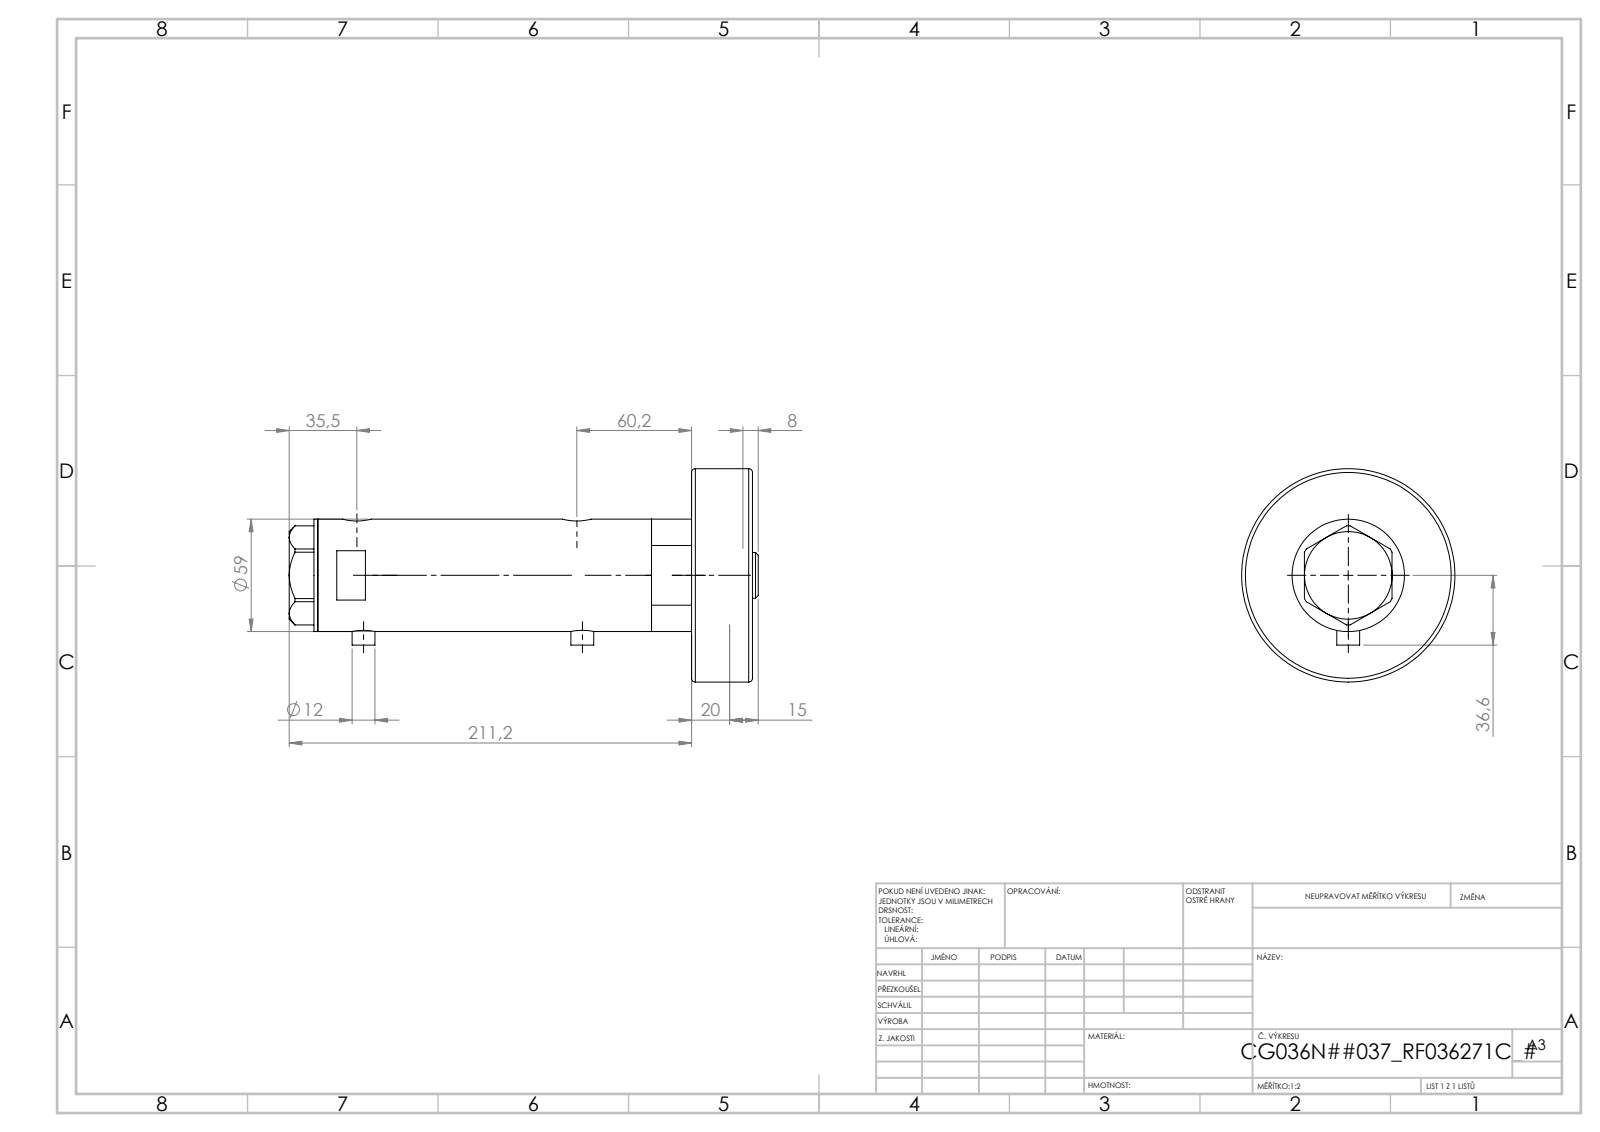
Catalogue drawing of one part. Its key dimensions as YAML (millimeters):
part_name: "V270CG_BACK; V270CG_MIDDLE; V270CG_VC; V270CG_FRONT"
step_written_by: "SolidWorks 2019 (CONFIG_CONTROL_DESIGN)"
units: millimeters
bodies: {solids: 4, faces: 126, planar: 53, cylindrical: 53, other: 20}
overall_size: [200.42, 60.1, 59]
volume: 452799
surface_area: 95842
round_holes:
  - {diameter: 5, count: 2}
  - {diameter: 9.73, count: 2}
  - {diameter: 12.5, count: 2}
  - {diameter: 15, count: 2}
  - {diameter: 8.5, count: 1}
  - {diameter: 25, count: 1}
  - {diameter: 26.5, count: 1}
  - {diameter: 36, count: 1}
  - {diameter: 40, count: 1}
  - {diameter: 52, count: 1}
round_bosses_or_shafts:
  - {diameter: 12, count: 2}
  - {diameter: 59, count: 1}
  - {diameter: 48, count: 1}
  - {diameter: 46, count: 1}
  - {diameter: 24, count: 1}
face_to_face_distances: [94.34, 23.5, 70.84, 15, 38.5, 109.34, 185.42, 170.42, 146.92, 76.08]
hole_center_spacings: [2.9, 3.5, 69.15, 72.05, 72.65, 75.55, 2.89, 2.91]
